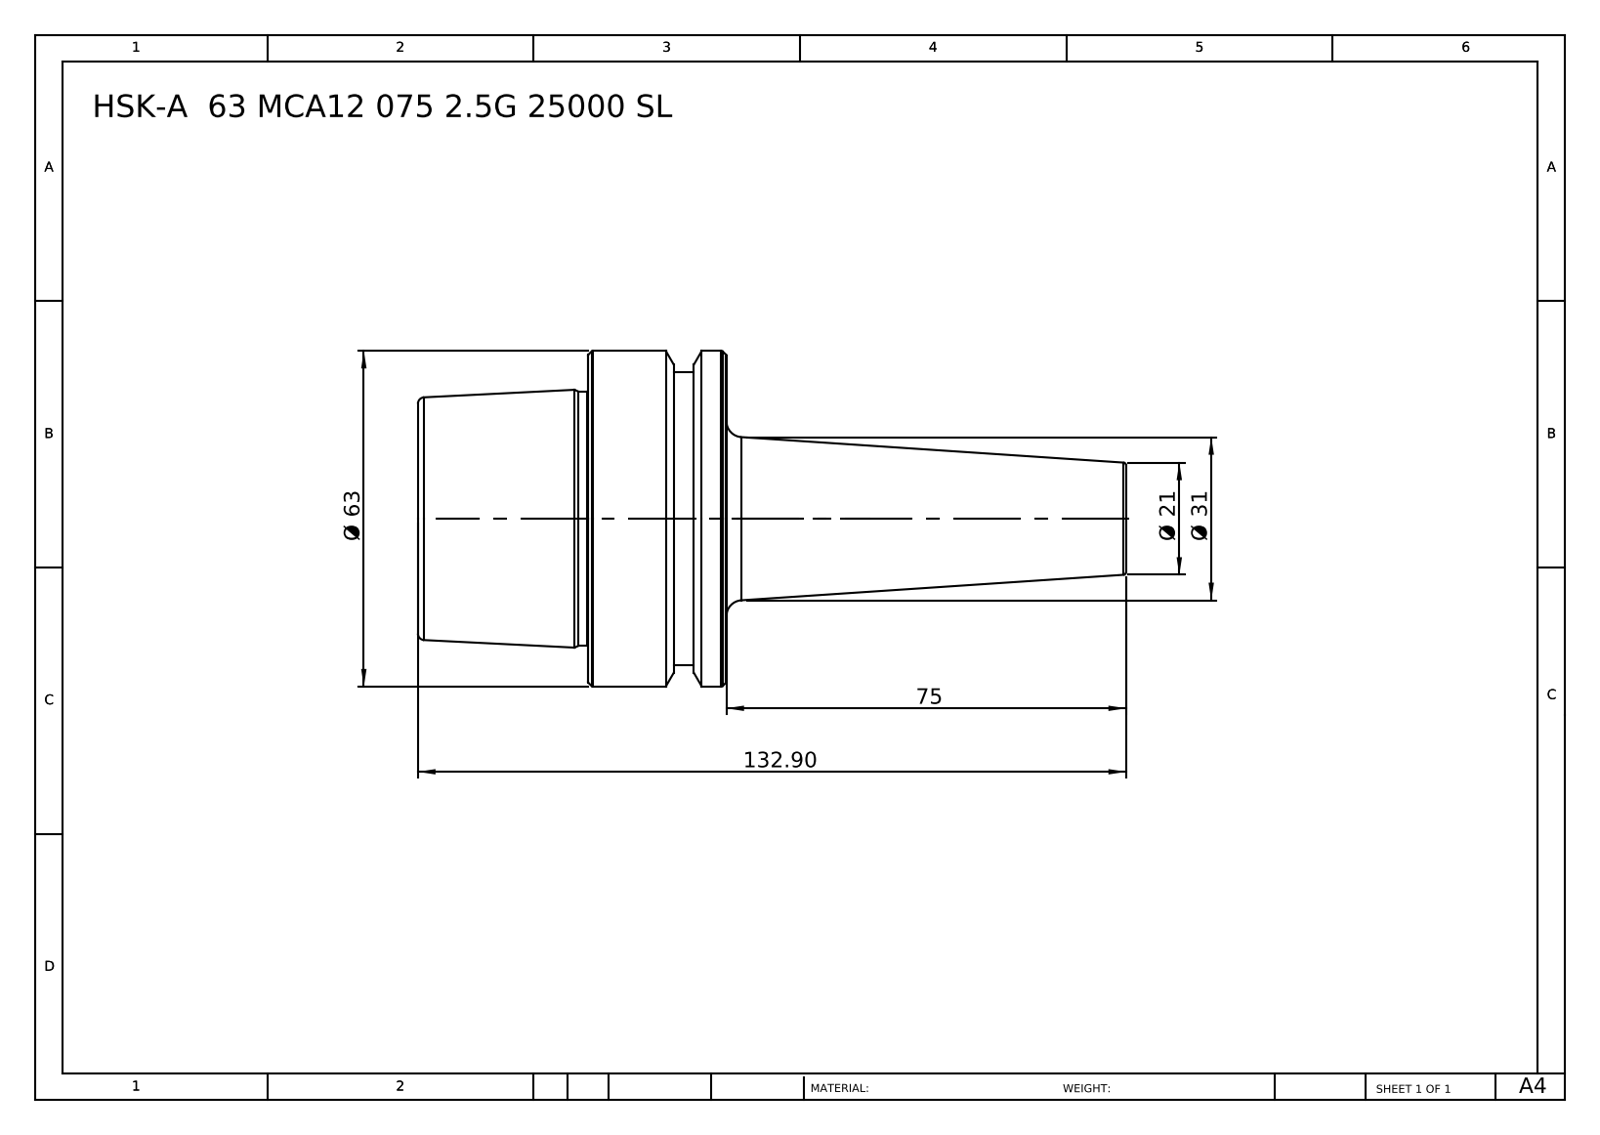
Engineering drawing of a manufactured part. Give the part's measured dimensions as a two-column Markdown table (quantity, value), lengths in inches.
| quantity | value |
| --- | --- |
| part name | HSK-A 63 MCA12 075 2.5G 25000 SL |
| STEP written by | SolidWorks 2014 (CONFIG_CONTROL_DESIGN) |
| units | inches |
| bodies | 1 solid, 46 faces (6 planar, 8 cylindrical, 32 other) |
| overall size | 5.232 × 2.48 × 2.48 |
| volume | 10.56 in³ |
| surface area | 34.51 in² |
| round bosses / shafts (diameter × count) | 2.48 × 1, 2.165 × 1, 1.881 × 1 |
| main face-to-face distances | 2.28, 1.024, 1.256, 2.953, 3.976, 5.232, 3.193, 0.24, 0.783, 2.039 |
